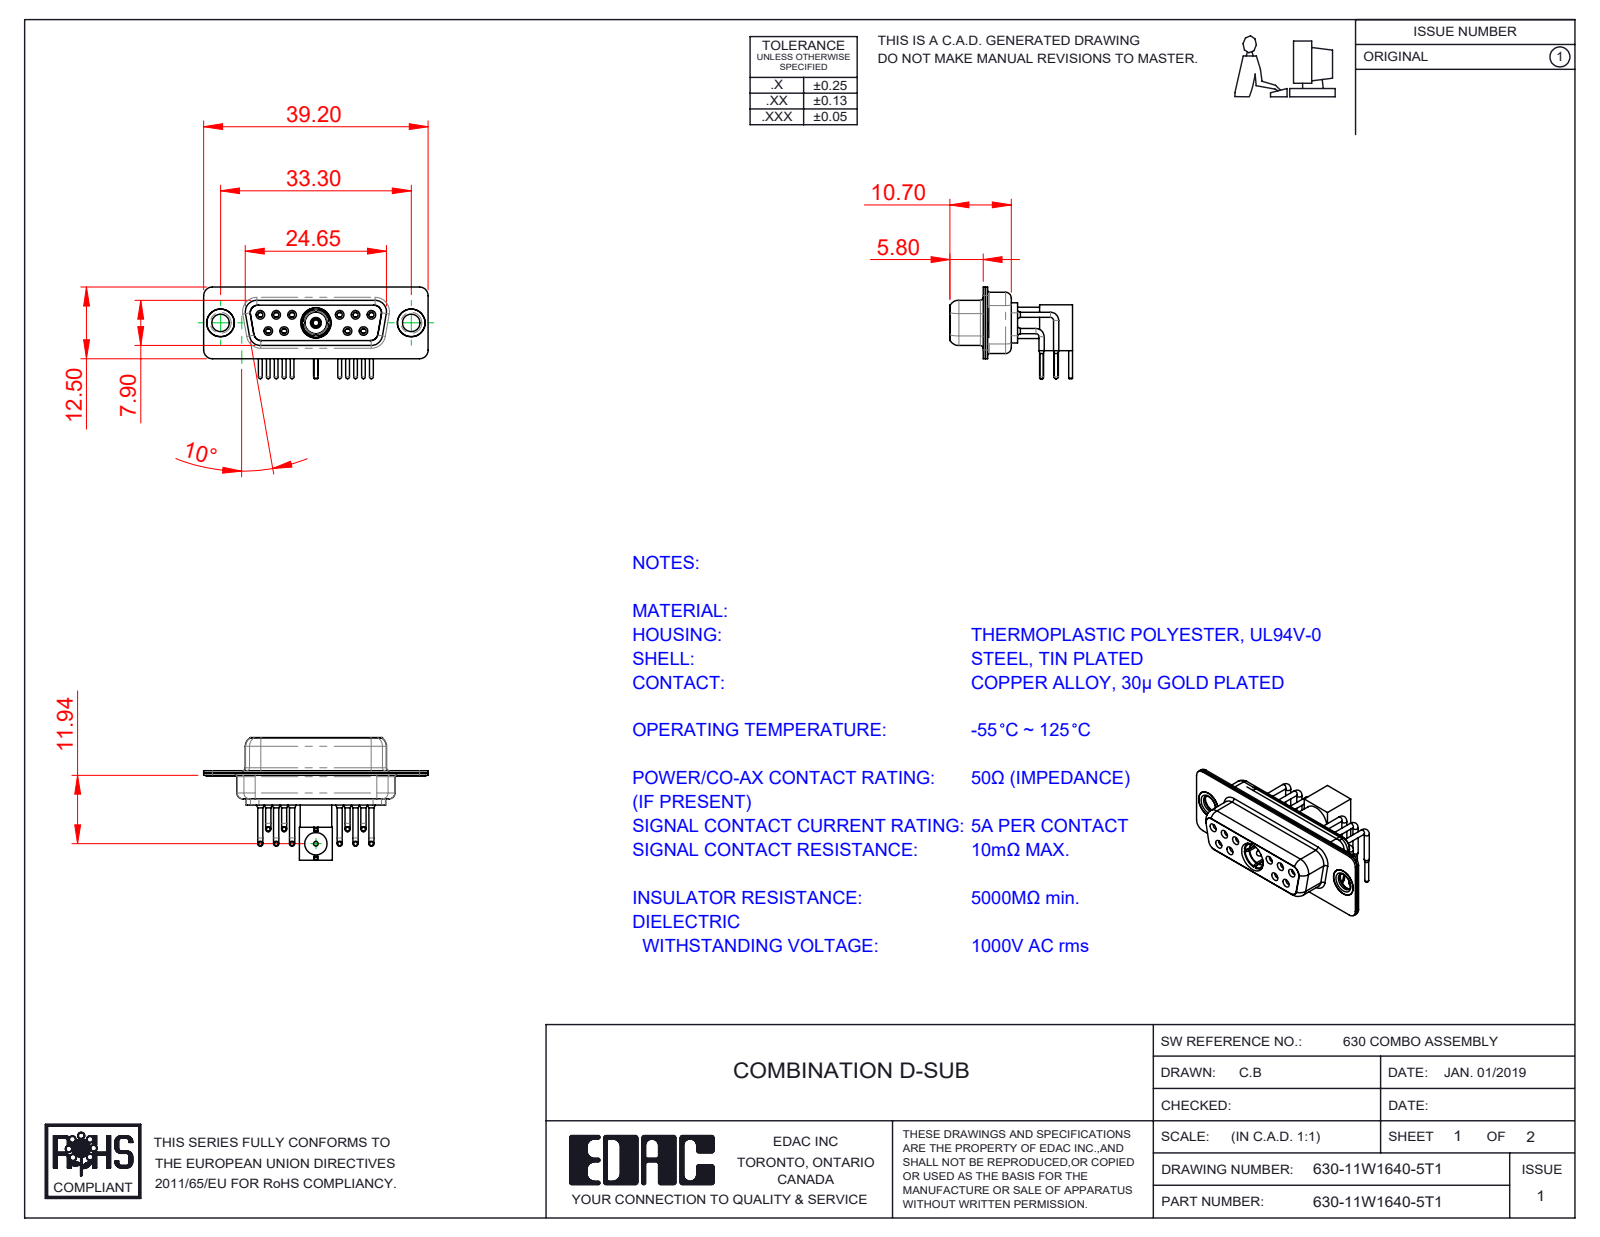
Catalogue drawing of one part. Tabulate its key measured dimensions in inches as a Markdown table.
| quantity | value |
| --- | --- |
| part name | 630Combo Shell Front_15 Contacts; 630Combo Contact Row 2; Co-Ax Plug Assy_RA; Locking Collar (+8 more) |
| STEP written by | SolidWorks 2020 (CONFIG_CONTROL_DESIGN) |
| units | inches |
| bodies | 21 solids, 951 faces (284 planar, 416 cylindrical, 251 other) |
| overall size | 1.543 × 0.843 × 0.63 |
| volume | 0.167 in³ |
| surface area | 10.46 in² |
| round holes (diameter × count) | 0.043 × 11, 0.059 × 11, 0.035 × 10, 0.079 × 10, 0.067 × 6, 0.063 × 4, 0.191 × 3, 0.12 × 2, 0.157 × 2, 0.159 × 2, 0.031 × 1, 0.111 × 1 |
| round bosses / shafts (diameter × count) | 0.035 × 10, 0.026 × 10, 0.063 × 6, 0.197 × 3, 0.195 × 2, 0.189 × 2, 0.14 × 2, 0.217 × 1 |
| partial cylindrical surfaces (radius × count) | 0.059 × 16, 0.053 × 12, 0.079 × 12, 0.063 × 8, 0.01 × 4, 0.02 × 4, 0.024 × 4, 0.026 × 4 |
| main face-to-face distances | 0.016, 0.055, 0.018, 0.071, 0.333, 0.35, 0.031, 0.244, 0.278, 0.073 |
| hole center spacings | 0.124, 0.109, 0.545, 0.436, 0.654, 0.198, 0.198, 0.218 |
